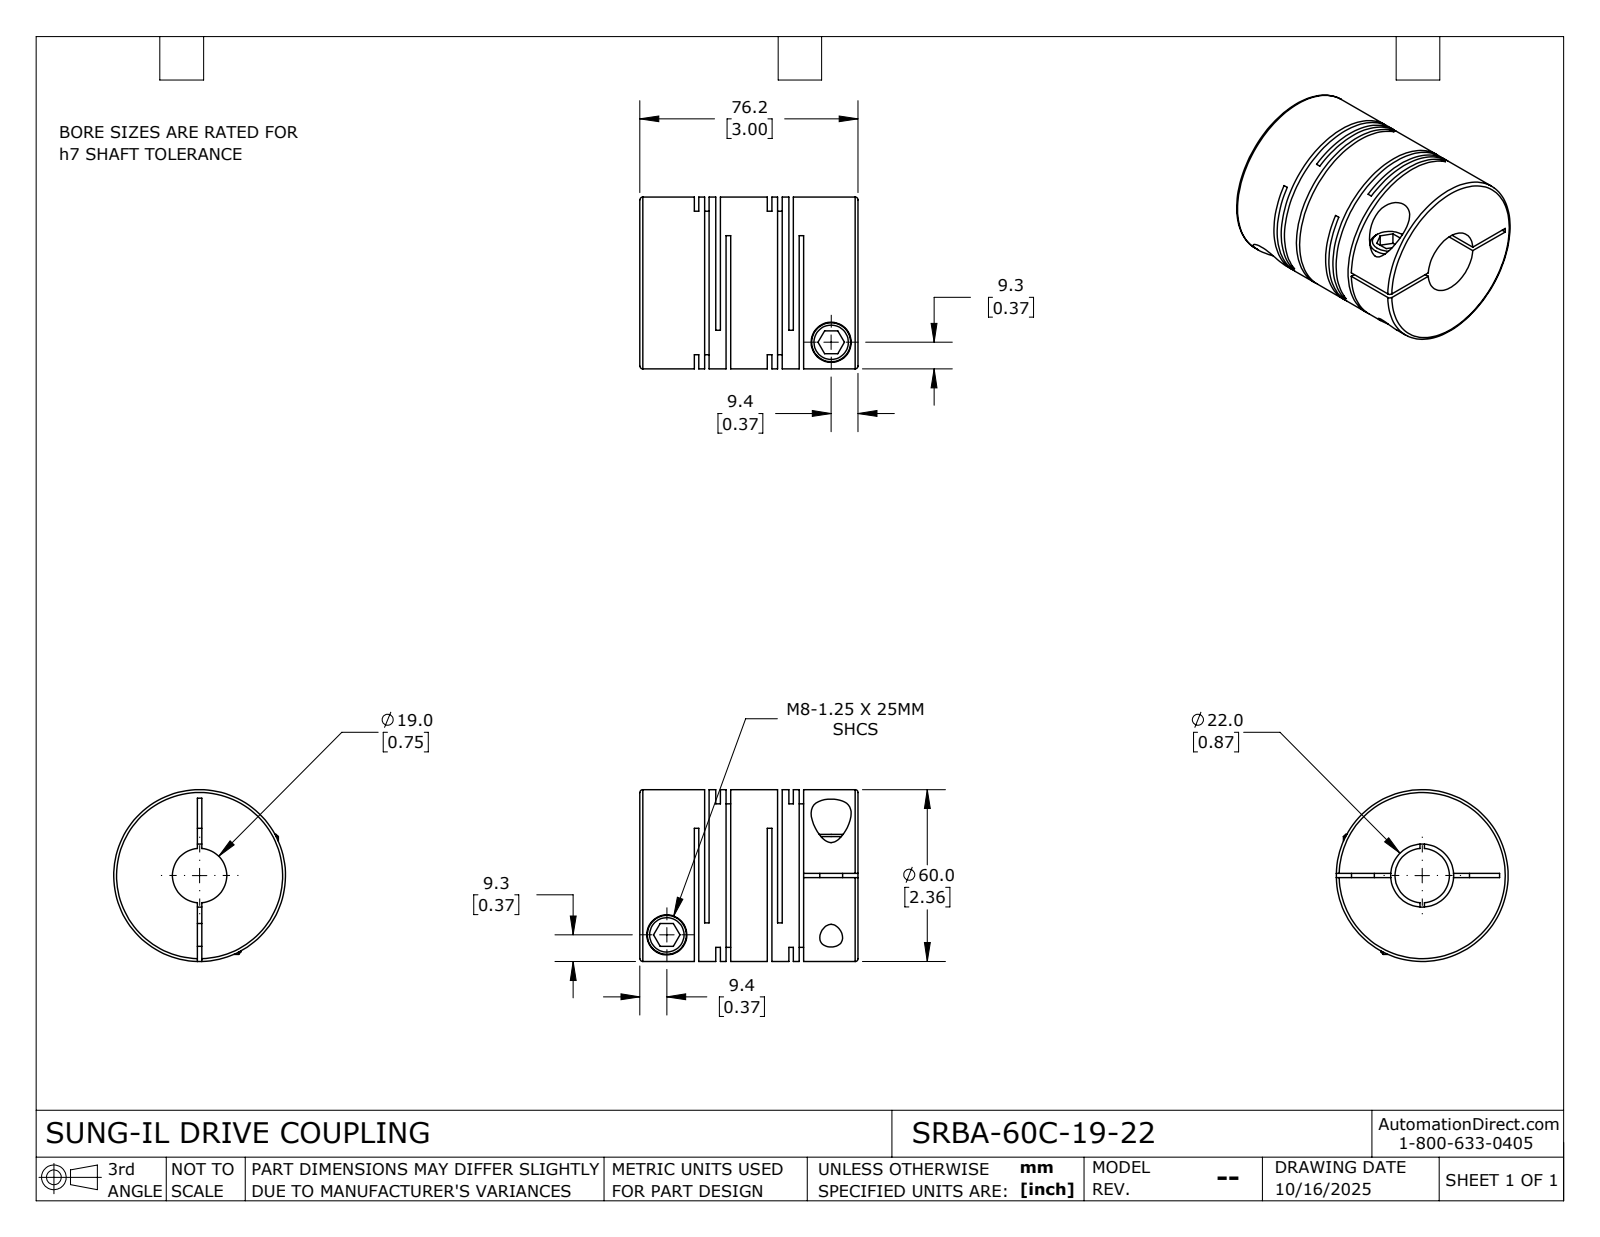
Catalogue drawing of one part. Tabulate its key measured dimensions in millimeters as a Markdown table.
| quantity | value |
| --- | --- |
| part name | SRBA-60C-19-22 |
| STEP written by | SolidWorks 2024 (CONFIG_CONTROL_DESIGN) |
| units | millimeters |
| bodies | 1 solid, 115 faces (60 planar, 42 cylindrical, 13 other) |
| overall size | 76.2 × 60 × 60 |
| volume | 157 959 mm³ |
| surface area | 58 311 mm² |
| round holes (diameter × count) | 8 × 2, 14 × 2, 19 × 1, 22 × 1 |
| round bosses / shafts (diameter × count) | 13.6 × 2, 60 × 1 |
| main face-to-face distances | 1.6, 3.6, 7.5, 25.5, 33, 2, 5.9, 3.9, 23.9, 21.9 |
